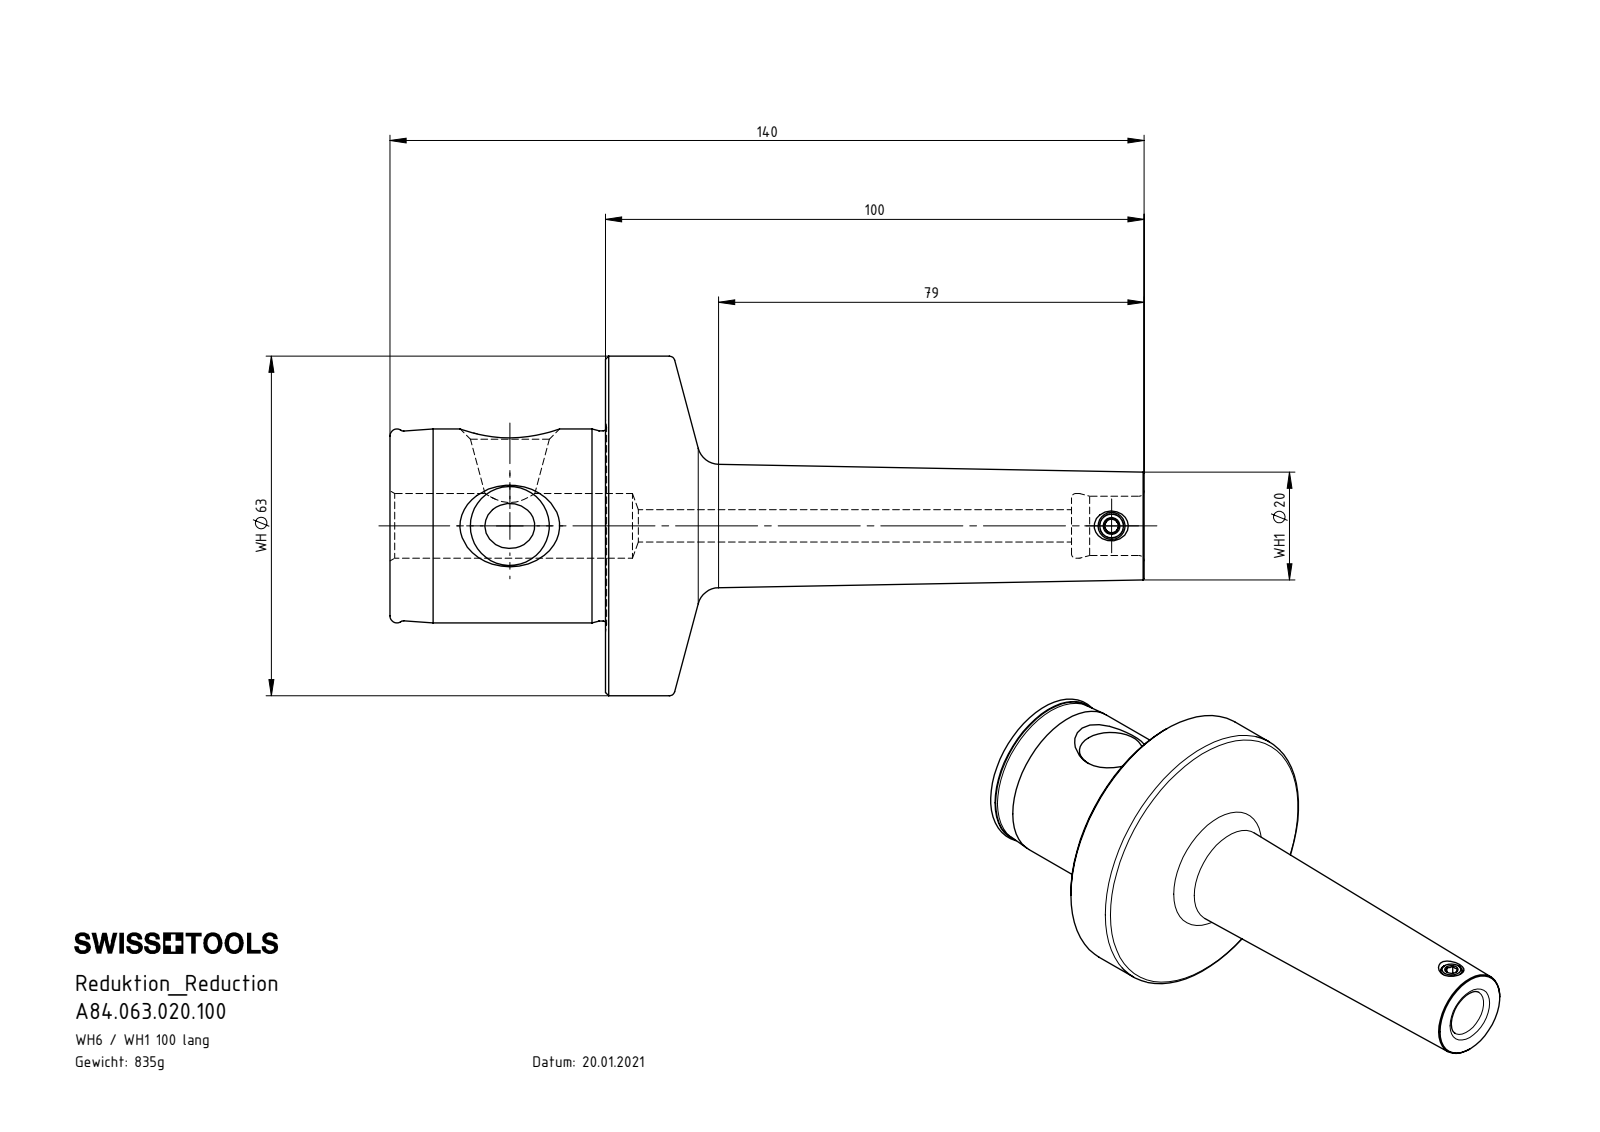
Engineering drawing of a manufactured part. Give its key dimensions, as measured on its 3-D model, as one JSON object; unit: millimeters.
{"part_name": "WH1-ER1.001.008; A84.063.020.100; WH6-WH1.K01.100_B", "step_written_by": "SolidWorks 2017 (CONFIG_CONTROL_DESIGN)", "units": "millimeters", "bodies": {"solids": 2, "faces": 100, "planar": 18, "cylindrical": 20, "other": 62}, "overall_size": [140, 63, 63], "volume_mm3": 107491, "surface_area_mm2": 22364, "round_holes": [[2.5, 1], [4.2, 1], [4.5, 1], [11, 1], [12, 1]], "round_bosses_or_shafts": [[63, 1], [36, 1], [35.3, 1], [5, 1]], "face_to_face_distances": [40, 140, 100, 126.5, 86.5, 13.5, 2.5, 7.5, 4.5, 3]}
